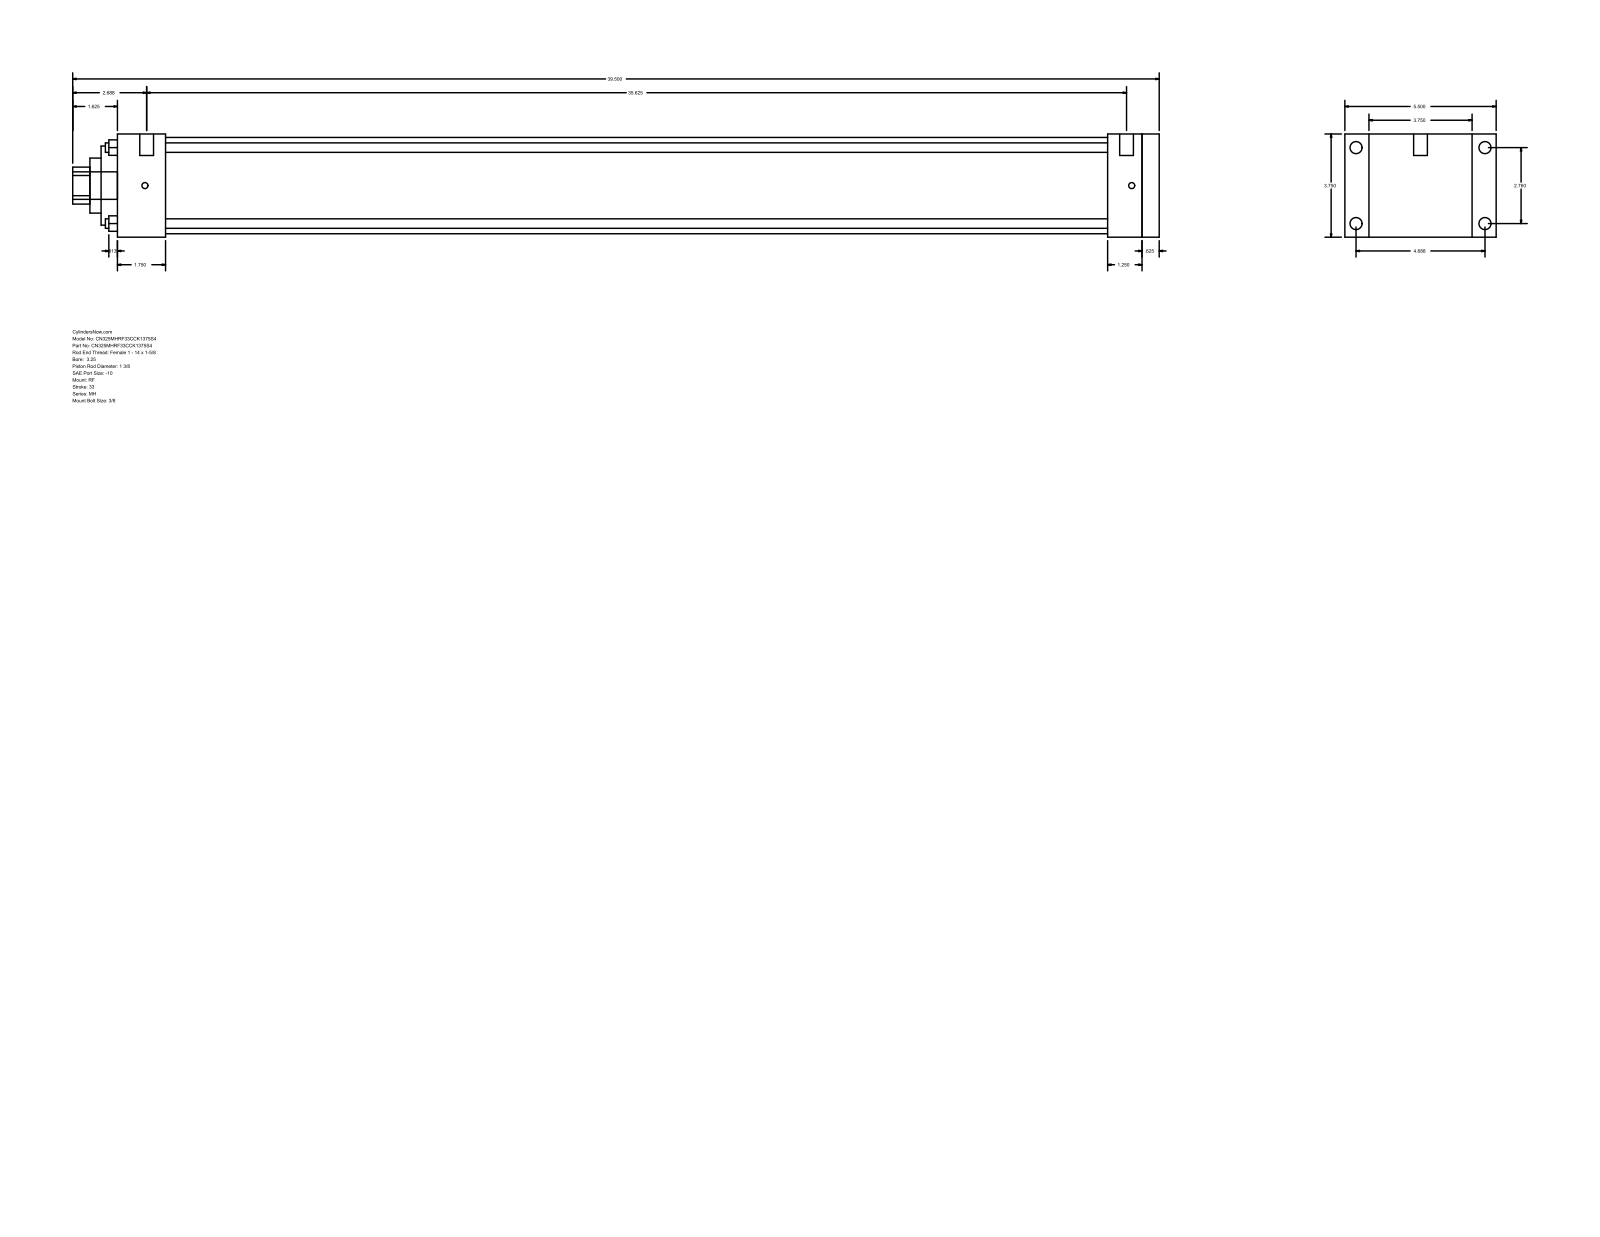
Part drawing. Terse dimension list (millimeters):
name: MH_RF__0325_1.375
written by: GSSL Pune (CONFIG_CONTROL_DESIGN)
unit: mm
bodies: 0 solids, 94 faces (65 planar, 29 cylindrical, 0 other)
size: 1003.3 × 139.7 × 95.25
holes: 4× ⌀8.76, 1× ⌀34.92, 1× ⌀50.8, 1× ⌀73.03, 1× ⌀88.9
bosses: 4× ⌀11.13, 4× ⌀5.56, 2× ⌀12.7, 1× ⌀25.4
rounds: 1× R17.06
face distances: 95.24, 962.03, 15.88, 946.15, 22.23, 117.47, 44.45, 901.7, 917.58, 914.4
hole spacings: 49.57, 70.1, 99.14
